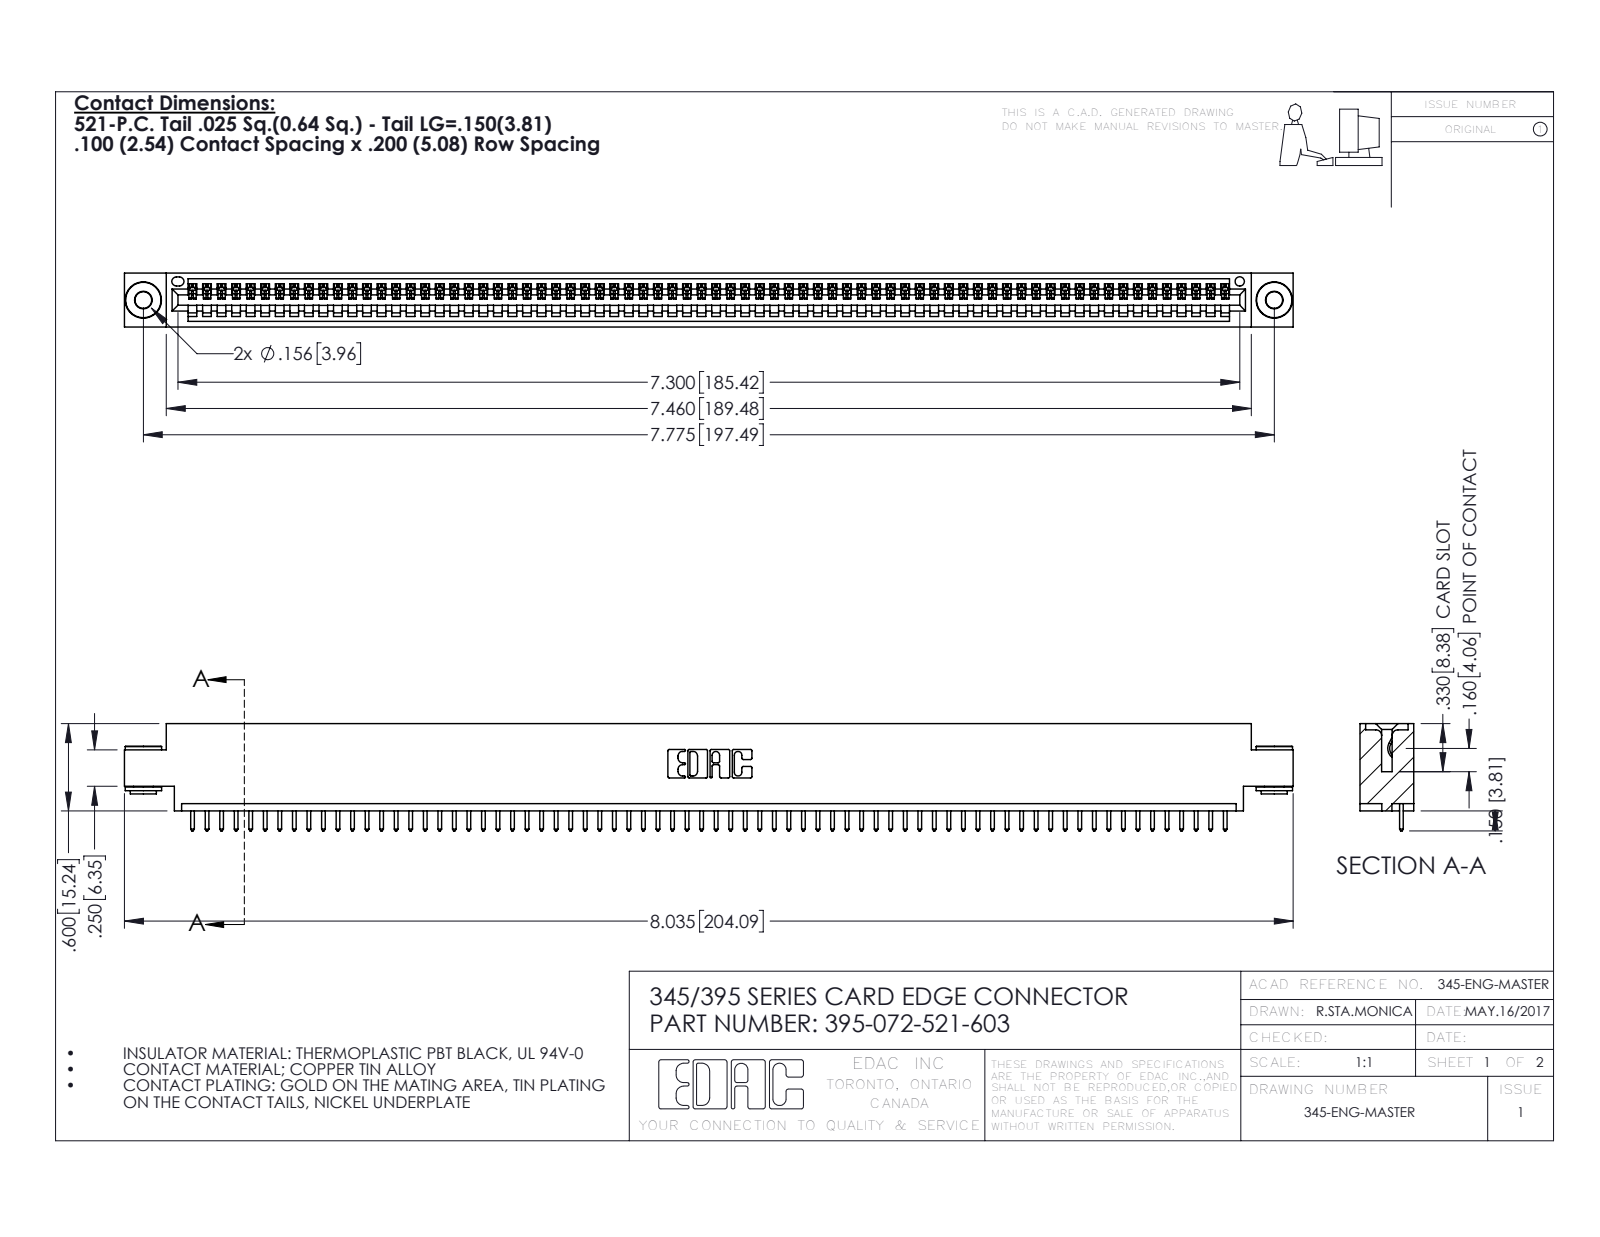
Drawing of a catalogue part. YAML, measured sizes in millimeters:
part_name: "395-072-521-603; 345-292-001_345-293-121; 345-250-002_345-250-002-102; 345 Part_0.170 Offset - 0.156 Dia-TH"
step_written_by: "SolidWorks 2016 (CONFIG_CONTROL_DESIGN)"
units: millimeters
bodies: {solids: 75, faces: 4344, planar: 2974, cylindrical: 1362, other: 8}
overall_size: [204.1, 18.7, 9.4]
volume: 19340
surface_area: 25640
round_holes:
  - {diameter: 2.9, count: 2}
  - {diameter: 4, count: 2}
  - {diameter: 1.6, count: 1}
round_bosses_or_shafts:
  - {diameter: 6.4, count: 2}
  - {diameter: 4.6, count: 2}
  - {diameter: 3.5, count: 2}
partial_cylinders:
  - {radius: 0.2, count: 144}
  - {radius: 0.3, count: 144}
  - {radius: 0.3, count: 22}
  - {radius: 0.2, count: 6}
  - {radius: 0.8, count: 6}
  - {radius: 0.7, count: 3}
  - {radius: 0.8, count: 2}
  - {radius: 1, count: 2}
face_to_face_distances: [1.8, 7.6, 9.4, 5.1, 2.5, 6.9, 0.6, 5.7, 4.4, 3.8]
hole_center_spacings: [6.9, 191.5, 197.5]
